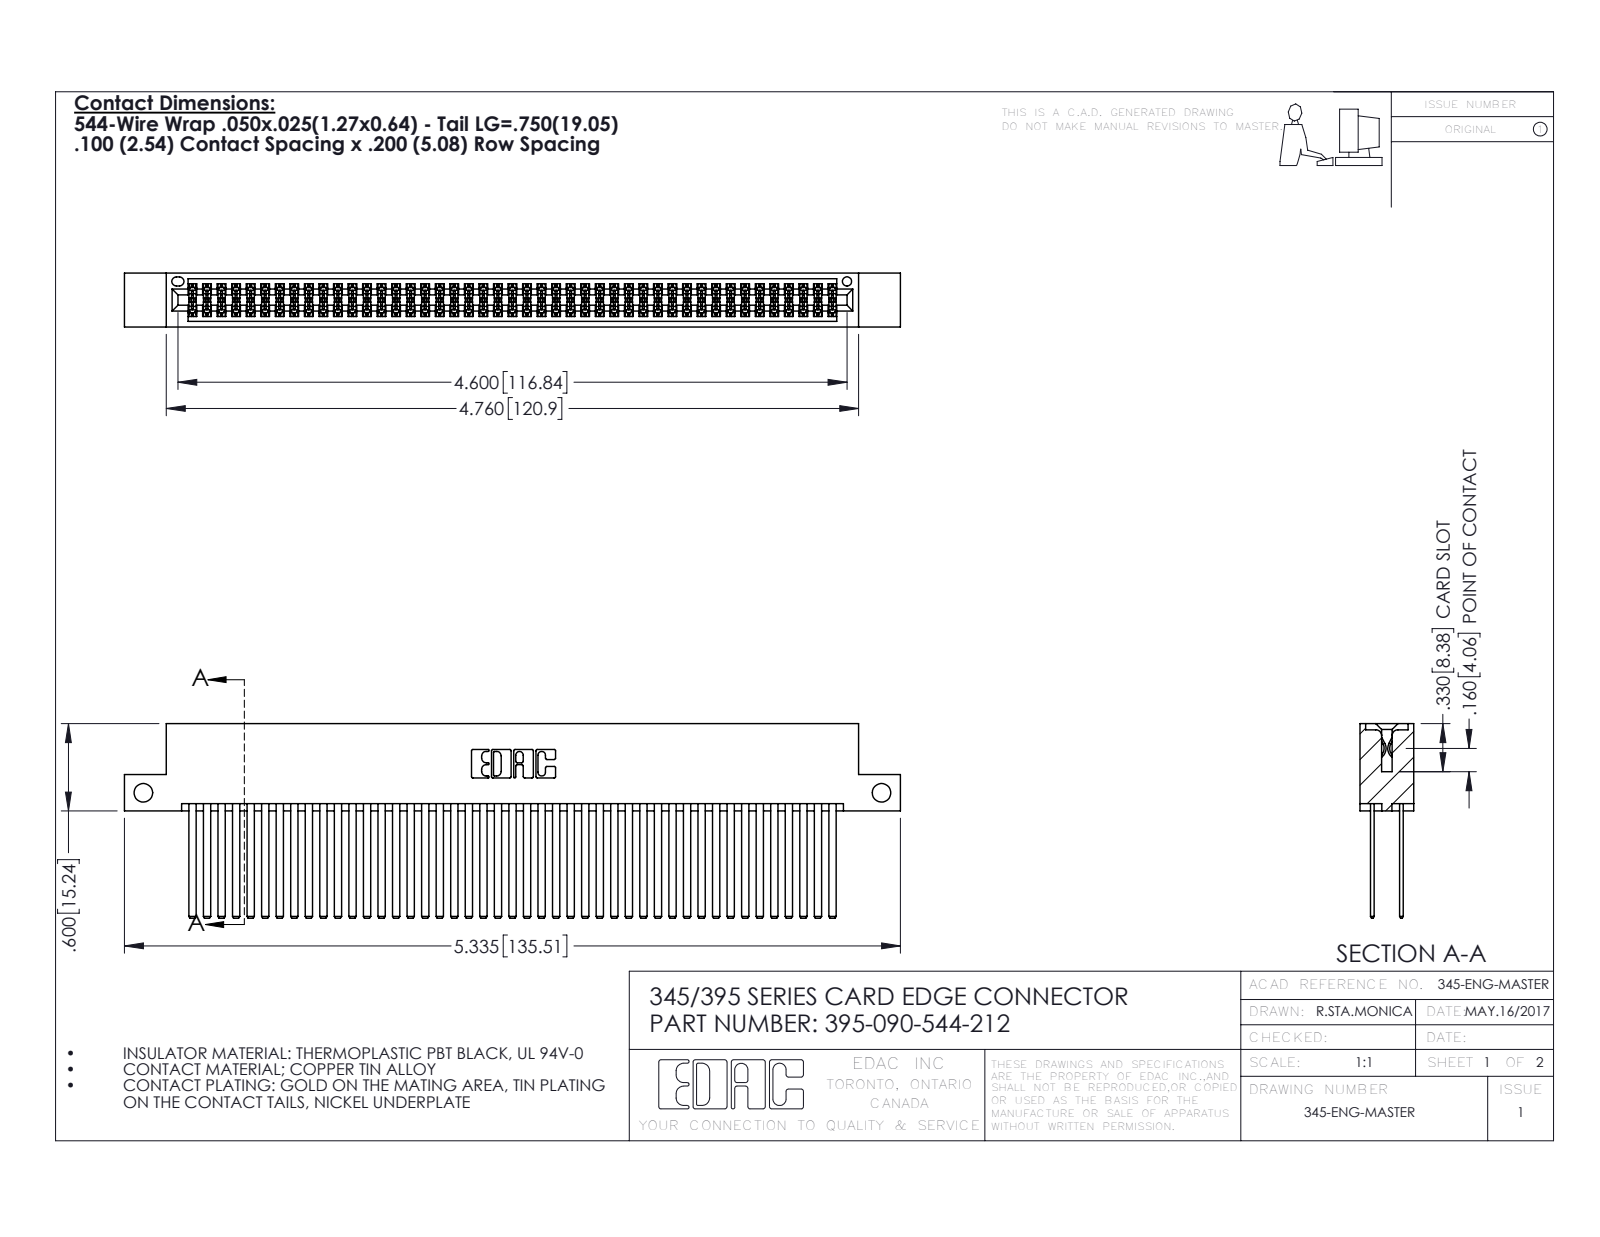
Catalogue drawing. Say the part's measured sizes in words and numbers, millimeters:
The part is named "395-090-544-212; 345 Part_Flush Mounting Lugs - Side Mount; 345-292-001_345-293-144". Its 3-D file was written by "SolidWorks 2016 (CONFIG_CONTROL_DESIGN)". It is 91 solids with 4086 faces: 2690 planar, 1396 cylindrical and 0 other. Overall it measures 135.5 by 34 by 9.4 millimeters. Its volume is 14 400 cubic millimeters and its surface area 24 860 square millimeters. Round holes: 2 of diameter 3.3, 1 of diameter 1.6. Partial cylindrical surfaces (rounded edges, fillets, slot ends): 135 of radius 0.2, 22 of radius 0.3, 6 of radius 0.2, 6 of radius 0.8, 3 of radius 0.7, 2 of radius 0.4, 2 of radius 0.5, 2 of radius 0.6. The main face-to-face distances are 5.1, 0.6, 7.6, 1.8, 2.5, 6.9, 5.7, 4.4, 9.4, 1.3. The hole center spacings are 128.9.
